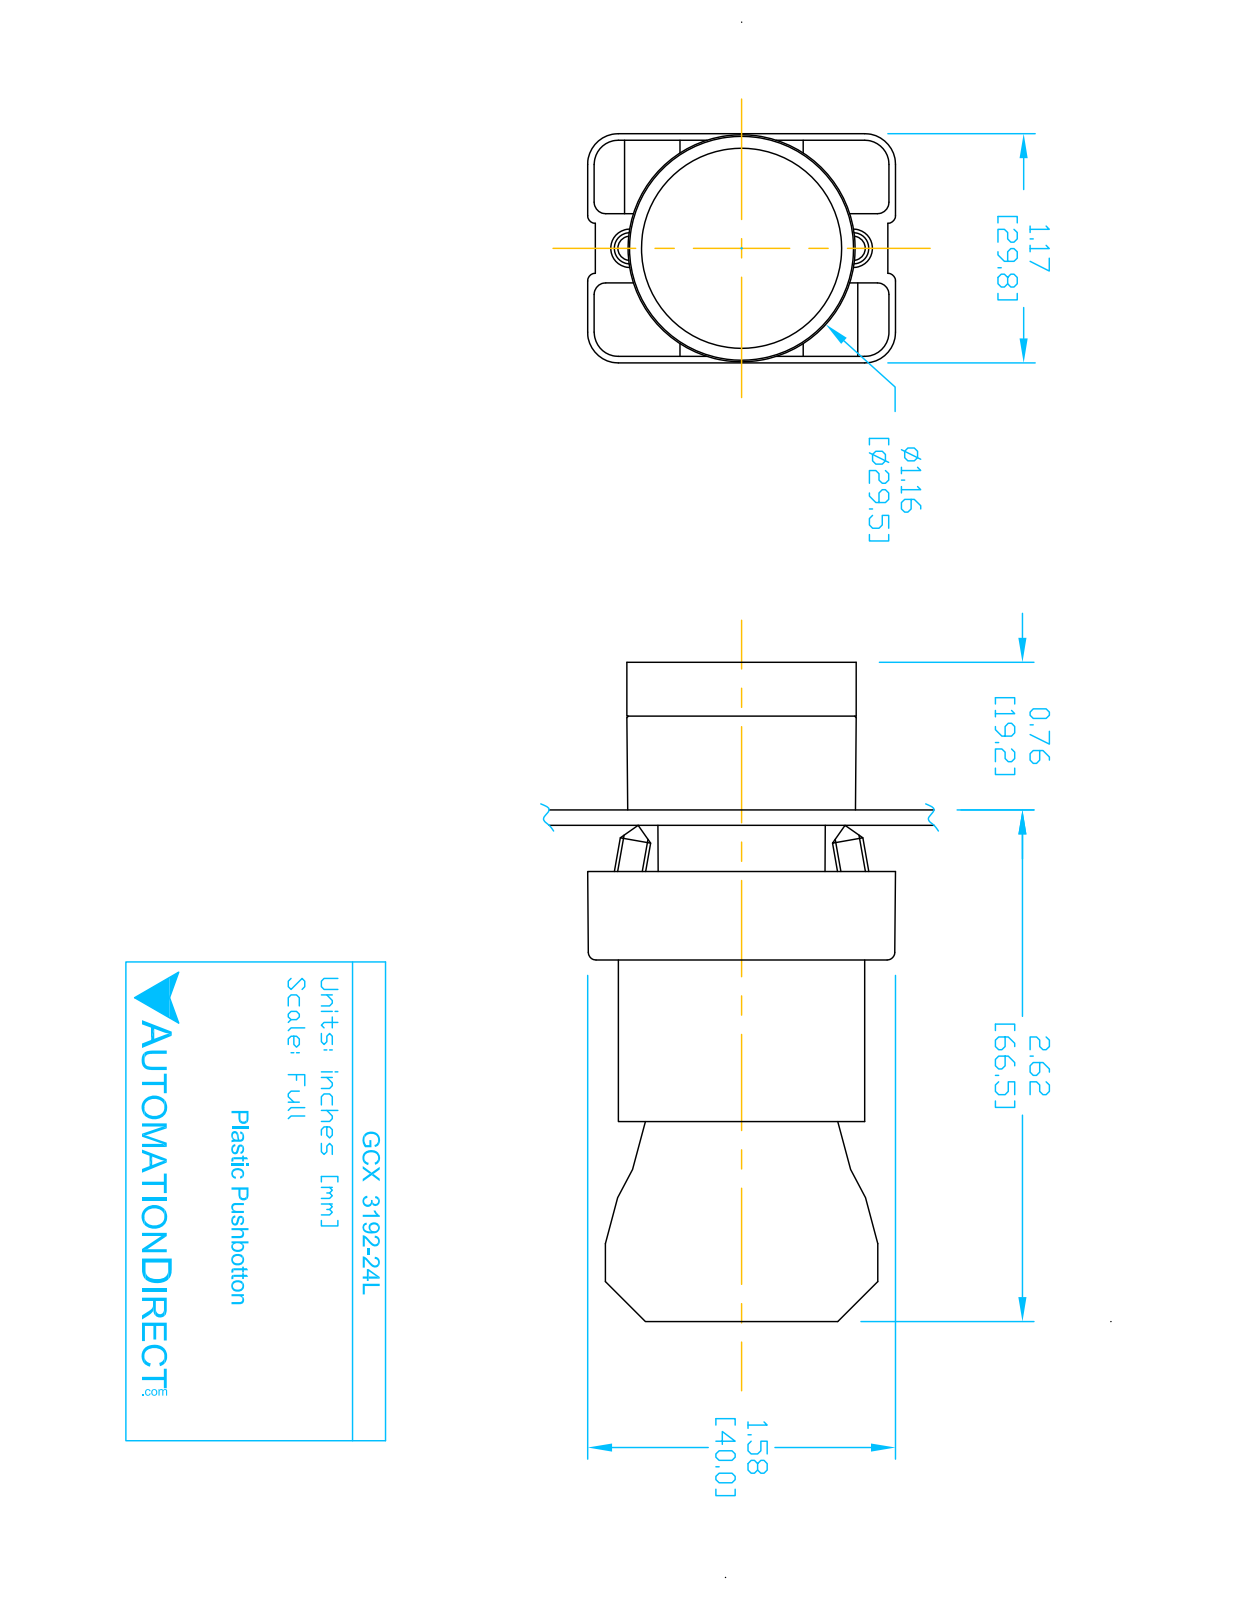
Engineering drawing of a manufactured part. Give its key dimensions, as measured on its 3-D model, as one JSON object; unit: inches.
{"part_name": "GCX3192L OPERATOR; ECX3029-2; CONTACT BLOCK; ECX1050 (+1 more)", "step_written_by": "SolidWorks 2016 (AUTOMOTIVE_DESIGN)", "units": "inches", "bodies": {"solids": 8, "faces": 431, "planar": 252, "cylindrical": 148, "other": 31}, "overall_size": [3.319, 1.581, 1.177], "volume_in3": 2.794, "surface_area_in2": 38.77, "round_holes": [[0.079, 2], [0.124, 2], [0.13, 2], [0.087, 1], [0.197, 1], [0.469, 1], [0.878, 1], [0.888, 1], [1.024, 1]], "round_bosses_or_shafts": [[0.157, 4], [1.175, 1], [1.004, 1], [0.945, 1], [0.856, 1], [0.78, 1], [0.504, 1]], "partial_cylinders_radius": [[0.059, 24], [0.041, 12], [0.124, 12], [0.157, 12], [0.039, 8], [0.128, 2], [0.02, 1], [0.063, 1]], "face_to_face_distances": [0.827, 0.579, 2.02, 1.193, 1.171, 0.276, 2.295, 1.469, 0.031, 0.033], "hole_center_spacings": [0.236, 0.544, 0.472, 0.49]}
